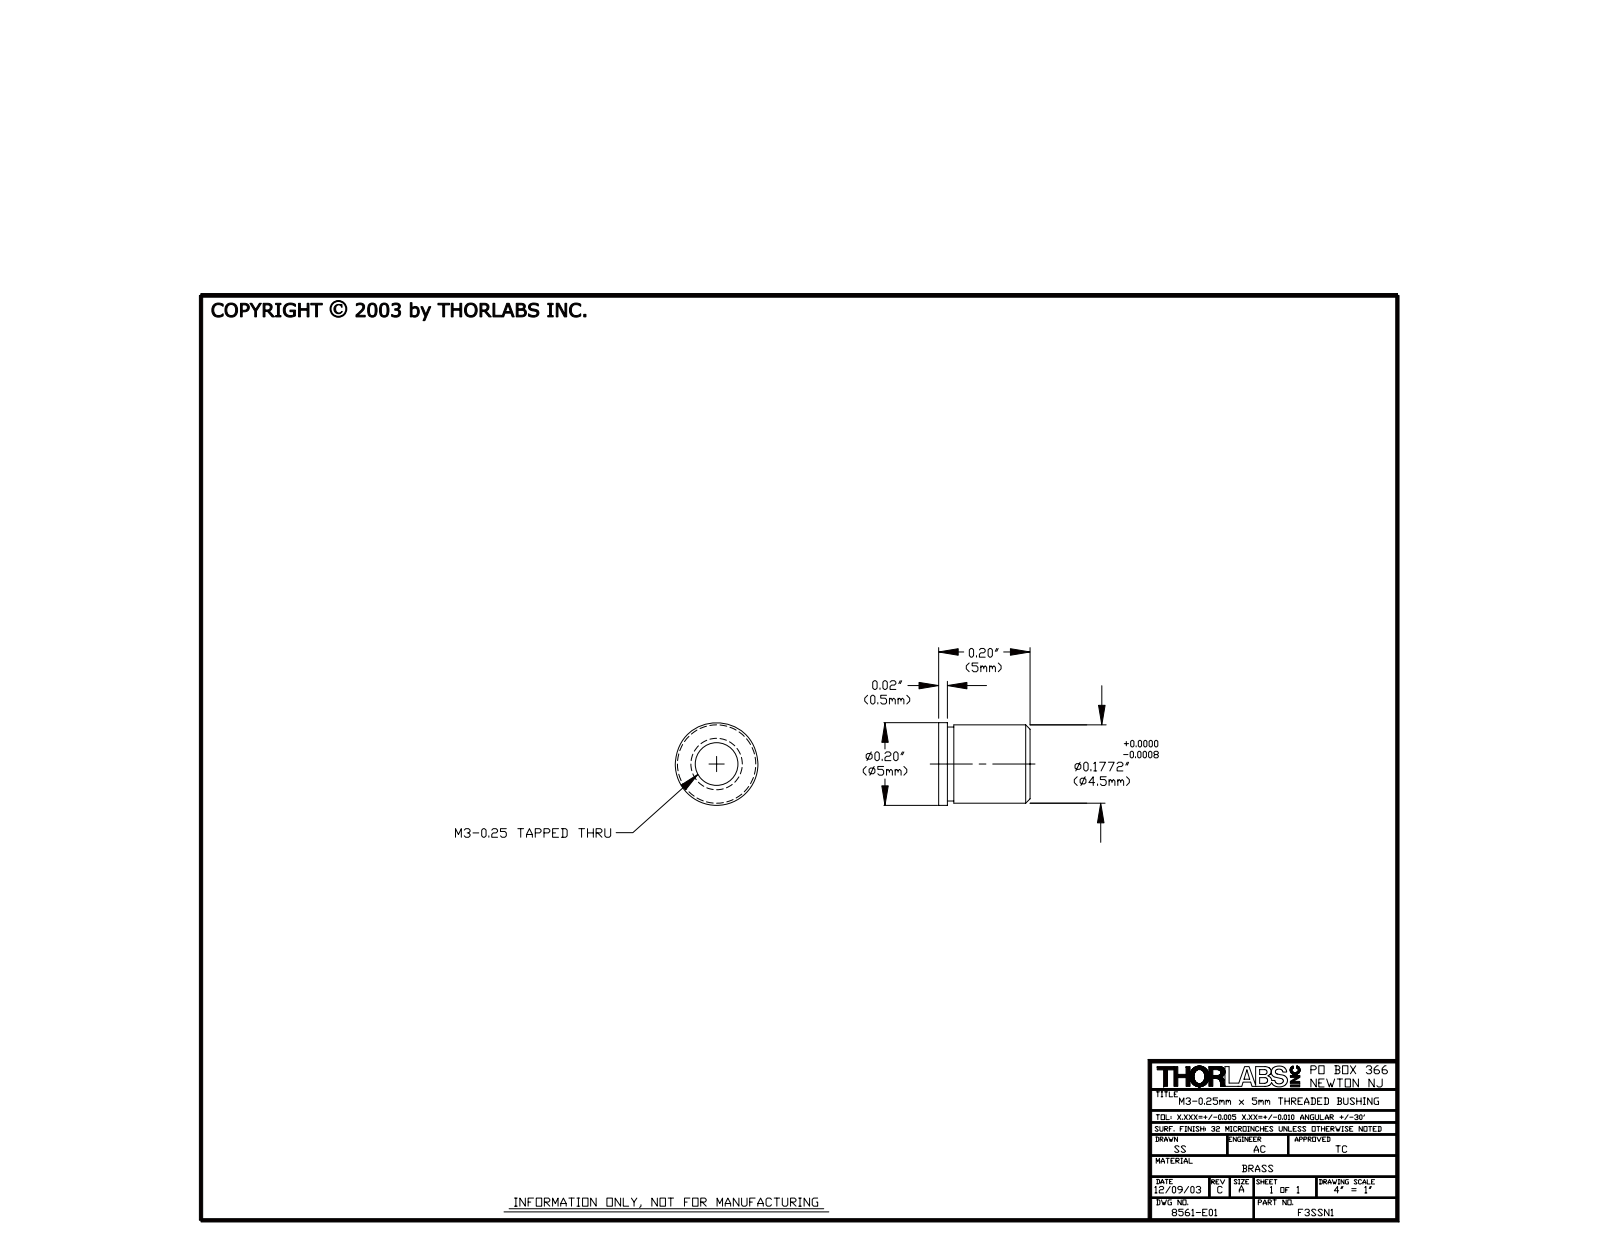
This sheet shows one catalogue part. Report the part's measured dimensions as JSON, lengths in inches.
{"part_name": "8561-E0W", "step_written_by": "SolidWorks 2007 (AUTOMOTIVE_DESIGN)", "units": "inches", "bodies": {"solids": 1, "faces": 11, "planar": 3, "cylindrical": 6, "other": 2}, "overall_size": [0.197, 0.197, 0.197], "volume_in3": 0.004, "surface_area_in2": 0.214, "round_holes": [[0.098, 1]], "round_bosses_or_shafts": [[0.197, 1], [0.178, 1]], "face_to_face_distances": [0.197, 0.177, 0.02]}
